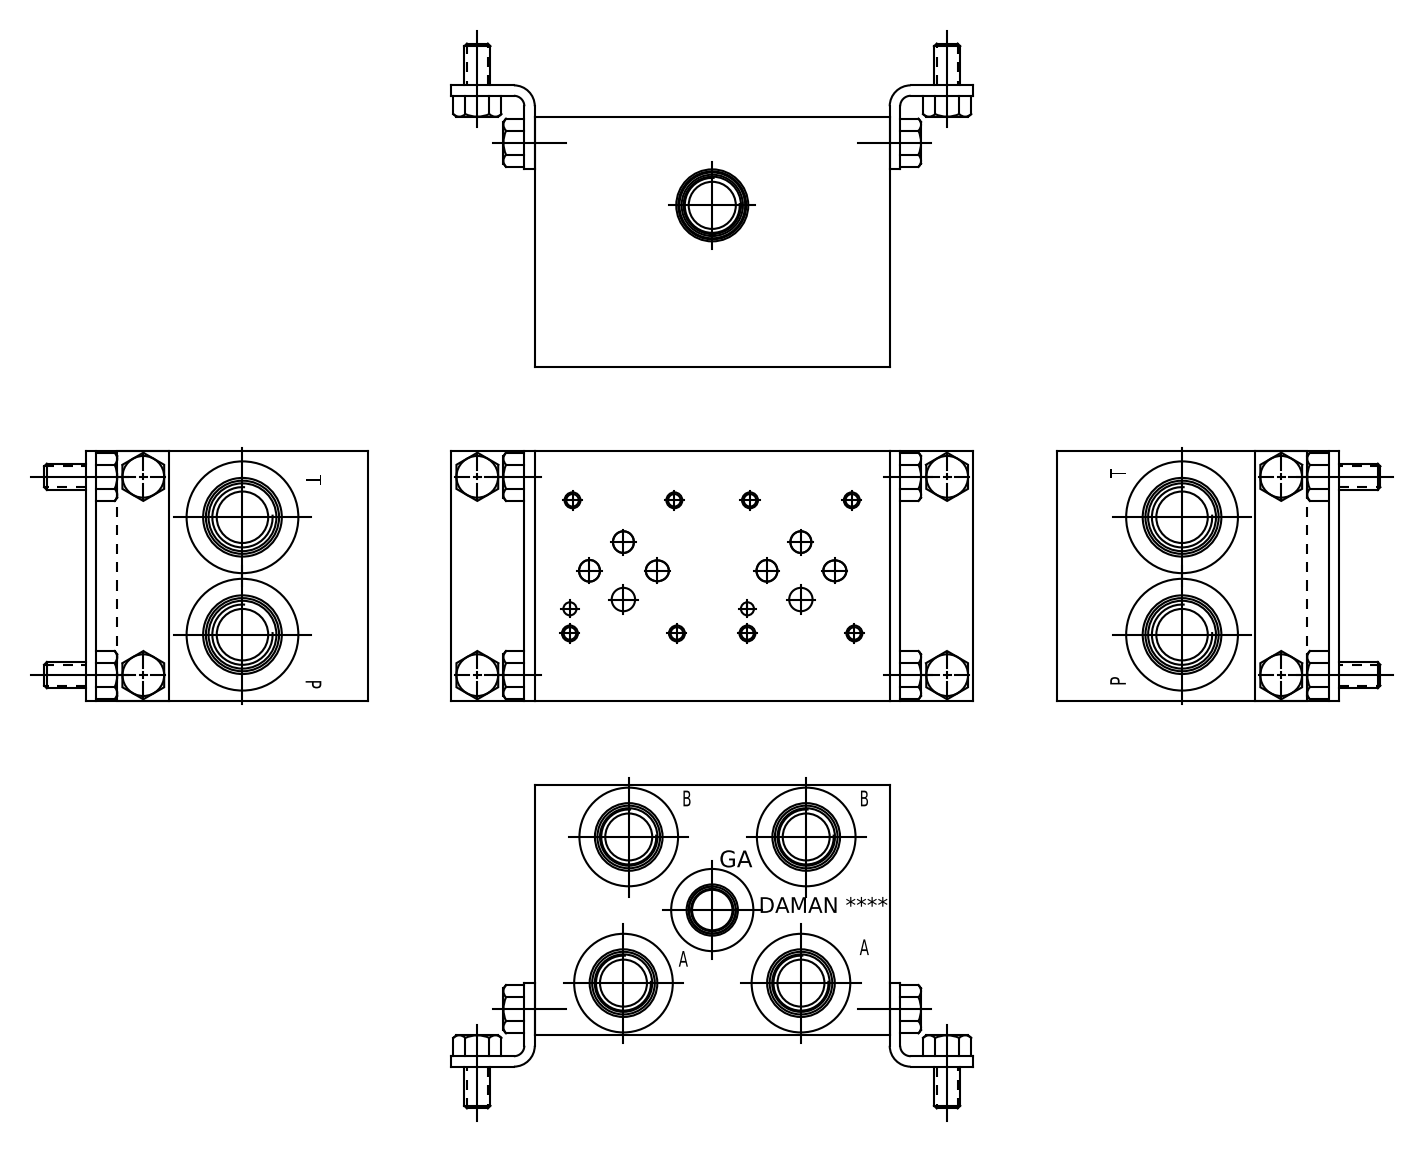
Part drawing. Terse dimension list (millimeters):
name: Part_AD03S022S_S_3D
written by: Autodesk Inventor 2020 (AUTOMOTIVE_DESIGN)
unit: mm
bodies: 1 solid, 698 faces (359 planar, 88 cylindrical, 251 other)
size: 107.95 × 76.2 × 76.2
volume: 537 131 mm³; area: 64 970 mm²
holes: 8× ⌀3.78, 8× ⌀4.83, 6× ⌀6.35, 4× ⌀14.3, 4× ⌀17.5, 4× ⌀19.05, 4× ⌀19.25, 4× ⌀30.63, 2× ⌀3.96, 2× ⌀6.53, 2× ⌀7.14, 2× ⌀7.92
face distances: 76.2, 107.95, 0.79, 75.41, 107.16, 106.37, 17.45, 90.5, 16.66, 89.71
hole spacings: 53.98, 22.05, 33.55, 40.5, 51.45, 53.97, 56.73, 7.5
